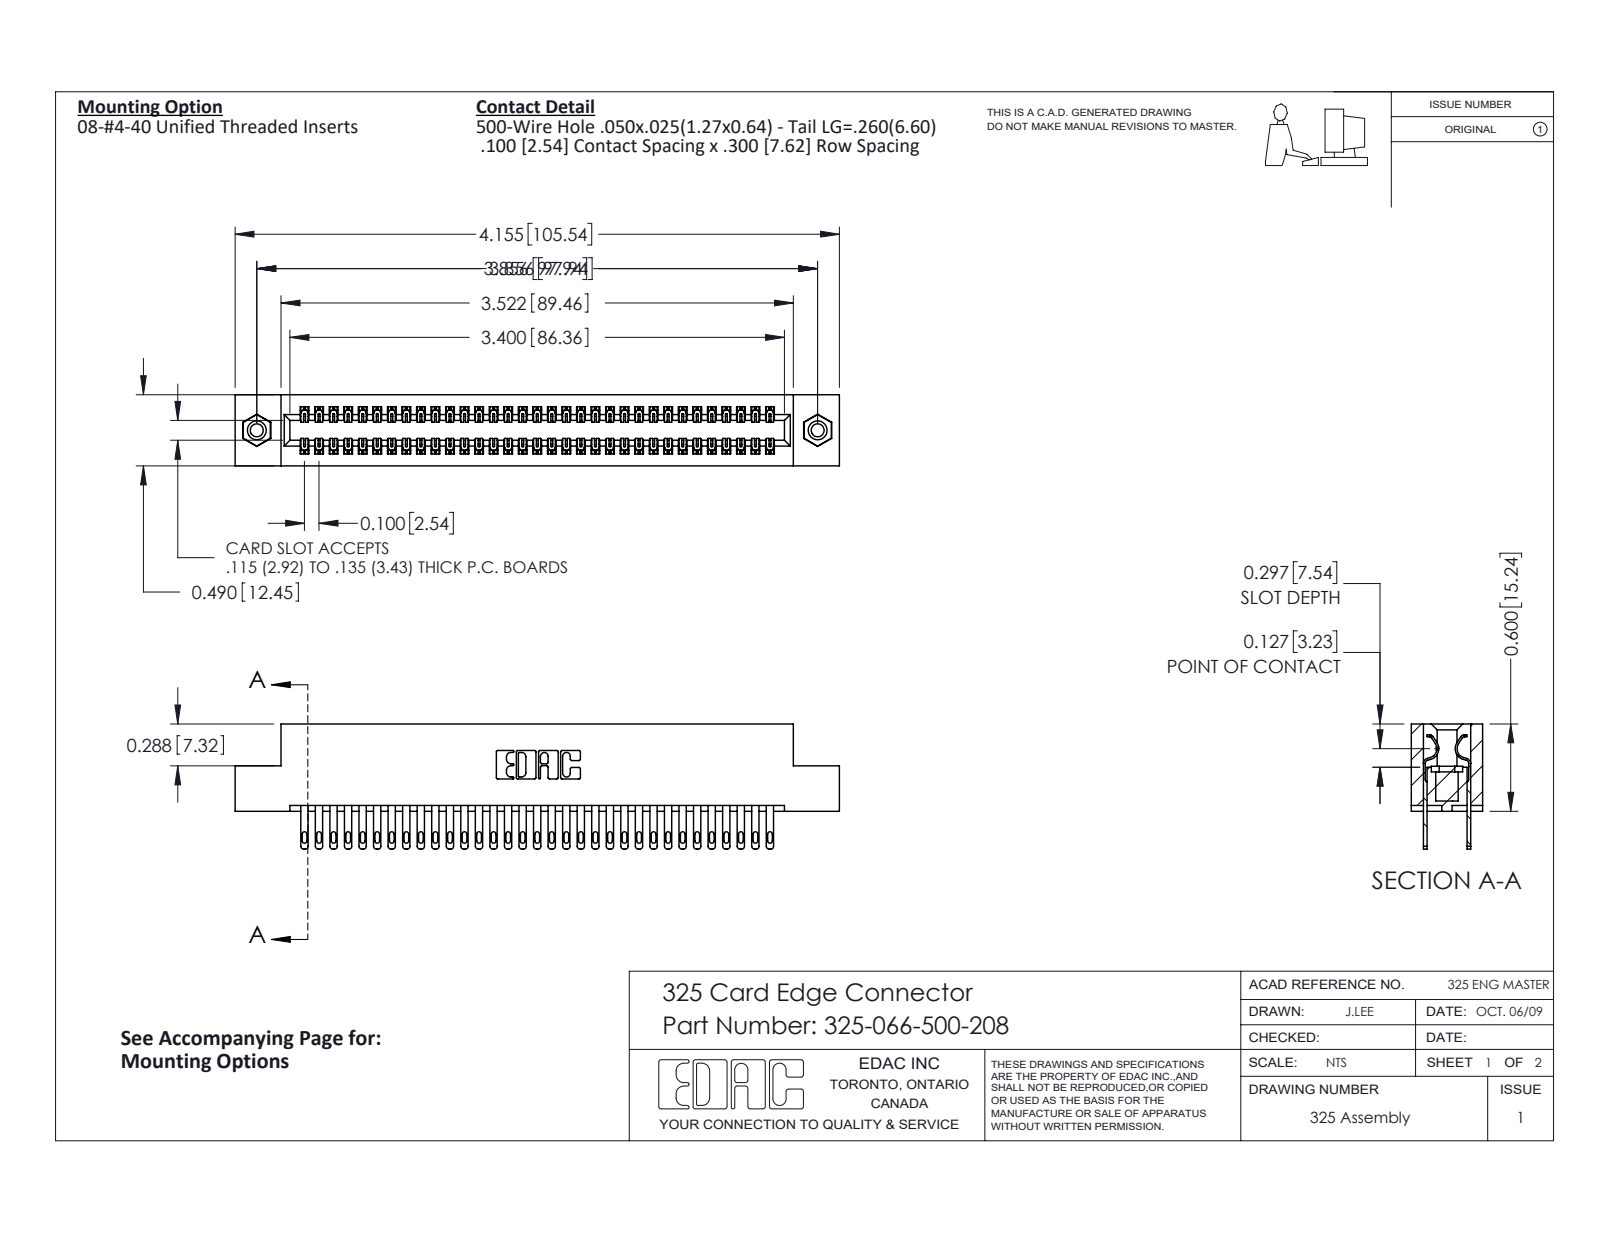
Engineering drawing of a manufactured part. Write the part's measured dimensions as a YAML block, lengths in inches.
part_name: "325-066-500-208; 345-250-001_345-250-003-102; 325 Part_TI; 325-292-001_325-293-100"
step_written_by: "SolidWorks 2016 (CONFIG_CONTROL_DESIGN)"
units: inches
bodies: {solids: 69, faces: 3342, planar: 2082, cylindrical: 1244, other: 16}
overall_size: [4.155, 0.86, 0.49]
volume: 0.838
surface_area: 26.53
round_holes:
  - {diameter: 0.089, count: 2}
  - {diameter: 0.125, count: 2}
  - {diameter: 0.16, count: 2}
round_bosses_or_shafts:
  - {diameter: 0.155, count: 2}
partial_cylinders:
  - {radius: 0.006, count: 99}
  - {radius: 0.016, count: 66}
  - {radius: 0.02, count: 66}
  - {radius: 0.01, count: 22}
  - {radius: 0.007, count: 6}
  - {radius: 0.031, count: 6}
  - {radius: 0.026, count: 3}
  - {radius: 0.014, count: 2}
face_to_face_distances: [0.083, 0.407, 0.3, 0.107, 0.383, 0.025, 0.49, 0.325, 0.275, 0.56]
hole_center_spacings: [3.856]
